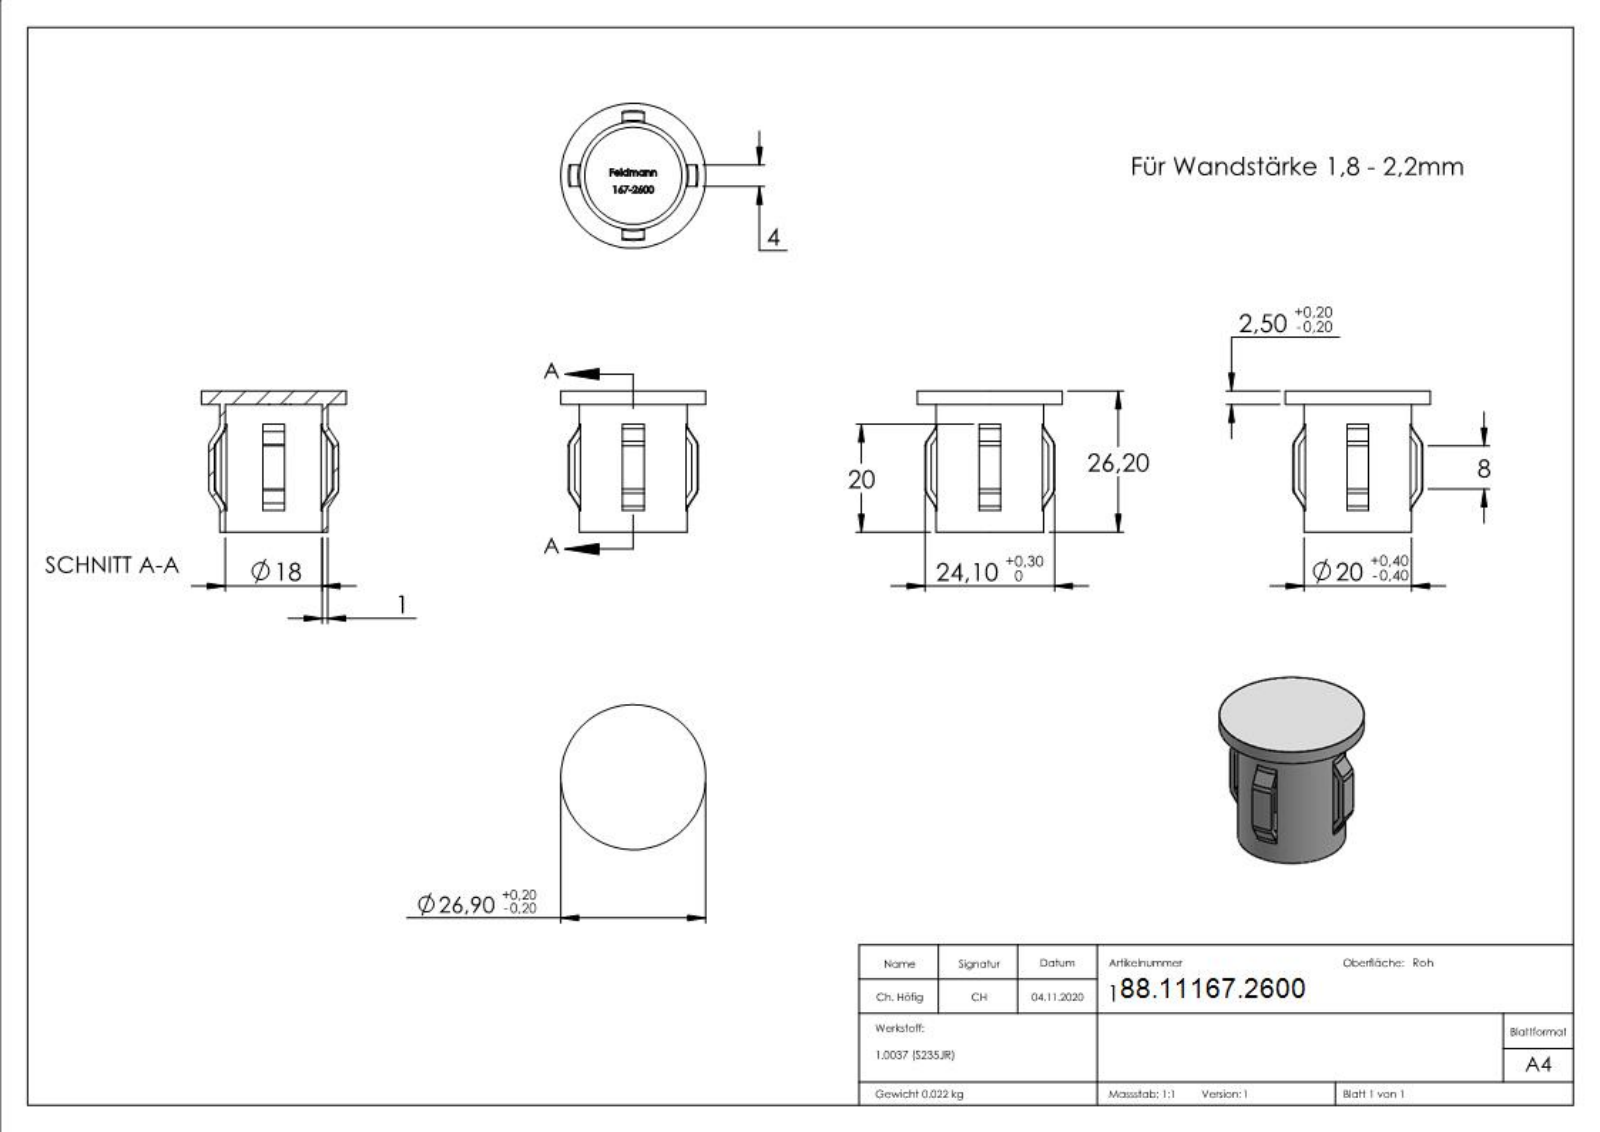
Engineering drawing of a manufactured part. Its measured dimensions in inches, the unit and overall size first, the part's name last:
Units: inches
Overall size (bounding box): 1.059 × 1.059 × 1.031
Round holes (diameter × count): ⌀0.709 ×1
Round bosses / shafts (diameter × count): ⌀1.059 ×1, ⌀0.787 ×1
Partial cylindrical surfaces — rounded edges, fillets, slot ends (radius × count): R0.407 ×1, R0.447 ×1
Main face-to-face distances: 0.098, 0.157, 0.933, 1.031, 0.094, 0.937, 0.117, 0.05, 0.015, 0.052
Volume: 0.173 in³ · Surface area: 6.836 in²
Bodies: 1 solid, 291 faces (125 planar, 16 cylindrical, 150 other)
Part name (STEP PRODUCT): 167-2600
STEP written by: SolidWorks 2018 (CONFIG_CONTROL_DESIGN)
